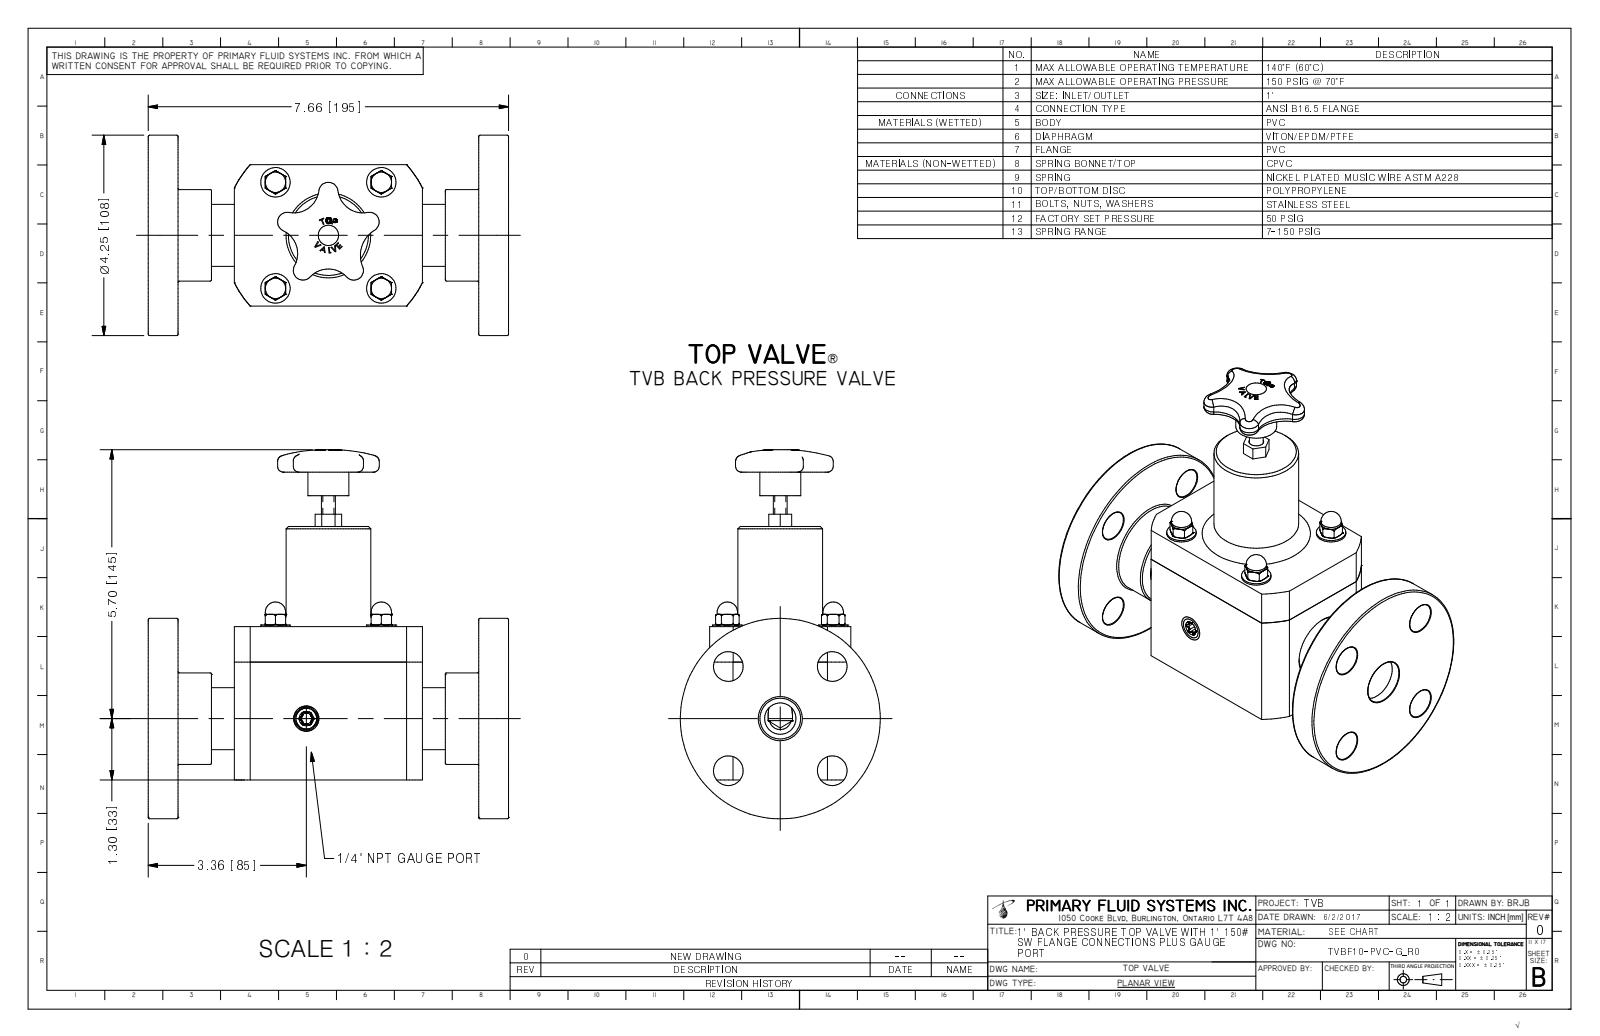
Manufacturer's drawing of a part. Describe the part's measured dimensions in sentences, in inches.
The part is named "TVBF10-PVC-G_R0". Its 3-D file was written by "Autodesk Inventor 2009 (AUTOMOTIVE_DESIGN)". It is 1 solid with 423 faces: 164 planar, 71 cylindrical and 188 other. Overall it measures 7.827 by 7.66 by 4.25 inches. Its volume is 62.78 cubic inches and its surface area 220.1 square inches. Round holes: 4 of diameter 0.175, 4 of diameter 0.63, 1 of diameter 0.936, 1 of diameter 0.957. Round bosses or shafts: 4 of diameter 0.625, 4 of diameter 0.433, 4 of diameter 0.375, 1 of diameter 4.25, 1 of diameter 1.941, 1 of diameter 1.8, 1 of diameter 1.315, 1 of diameter 0.87. Partial cylindrical surfaces (rounded edges, fillets, slot ends): 6 of radius 0.027, 5 of radius 0.085, 5 of radius 0.205, 4 of radius 0.536, 4 of radius 0.656, 1 of radius 0.625, 1 of radius 0.745, 1 of radius 2.238. The main face-to-face distances are 0.635, 7.025, 7.66, 3, 1.83, 5.83, 1.195, 5.195, 6.39, 3.25. The hole center spacings are 1.562, 2.209, 2.25, 3.125, 3.182.
